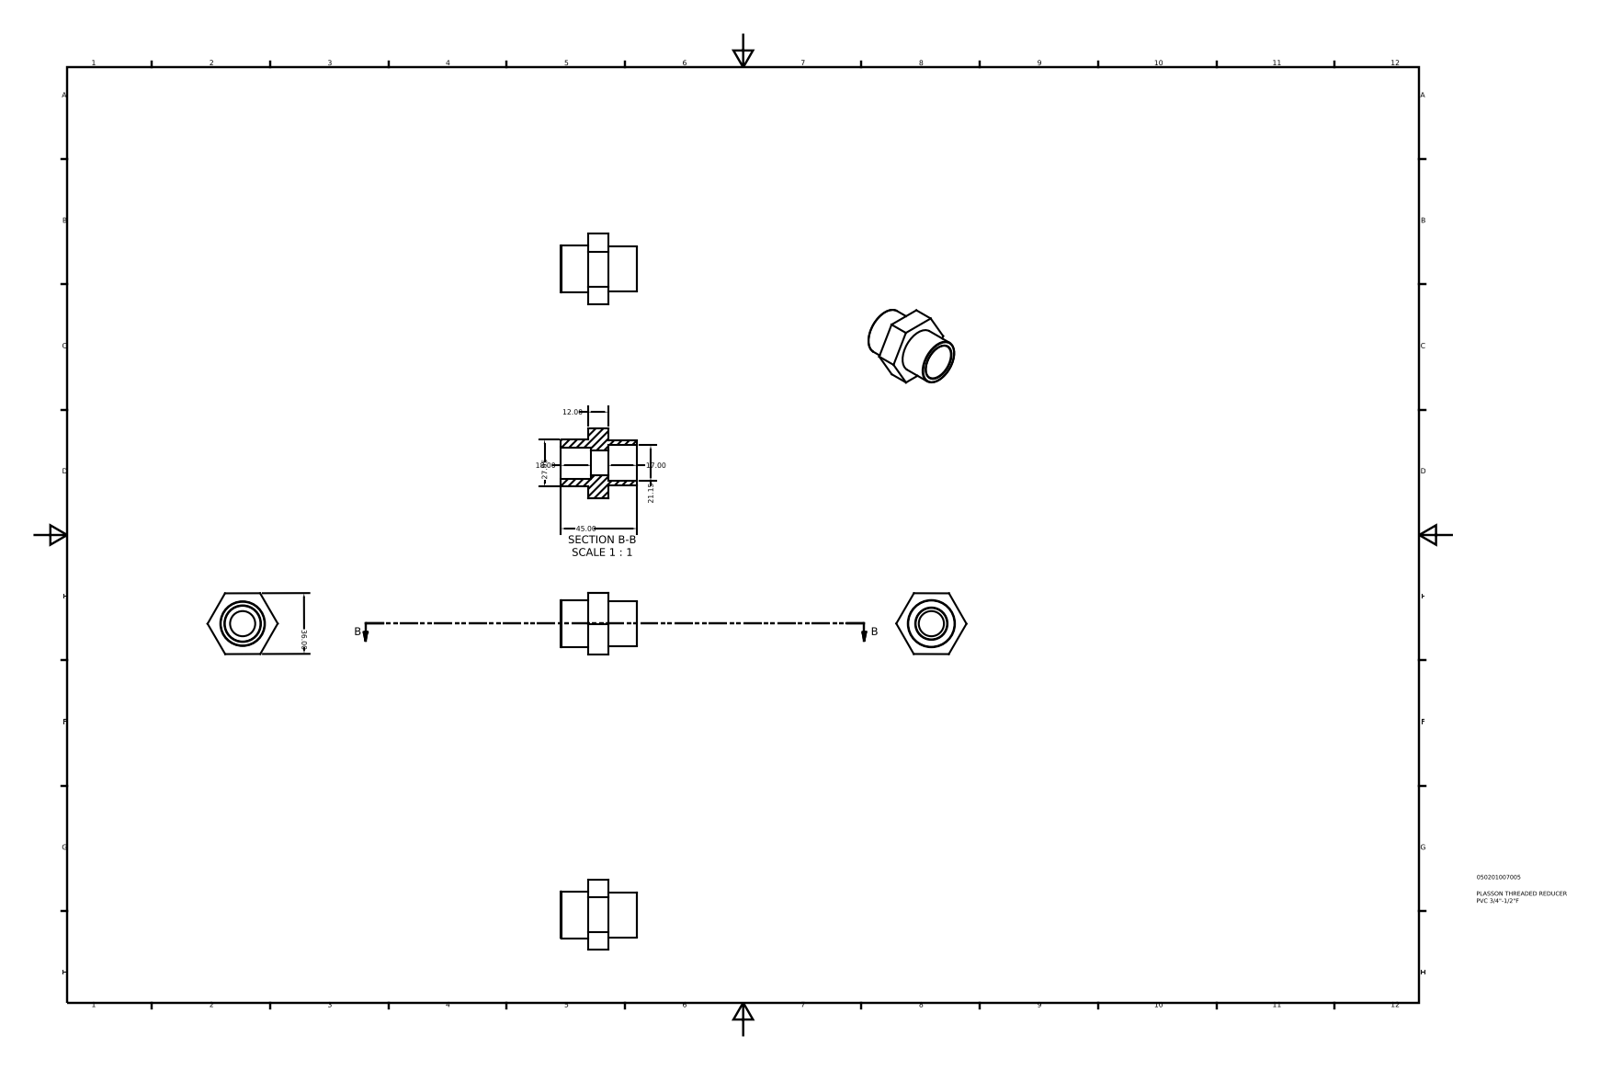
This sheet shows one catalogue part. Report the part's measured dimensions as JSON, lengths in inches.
{"part_name": "050201007005", "step_written_by": "Autodesk Inventor 2015 (AUTOMOTIVE_DESIGN)", "units": "inches", "bodies": {"solids": 1, "faces": 21, "planar": 12, "cylindrical": 5, "other": 4}, "overall_size": [1.772, 1.637, 1.42], "volume_in3": 1.22, "surface_area_in2": 13.68, "round_holes": [[0.587, 1], [0.733, 1], [0.833, 1]], "round_bosses_or_shafts": [[1.1, 1], [1.041, 1]], "face_to_face_distances": [0.472, 1.418, 0.63, 1.102, 1.417, 1.772, 1.142, 0.669, 0.709, 0.079]}
